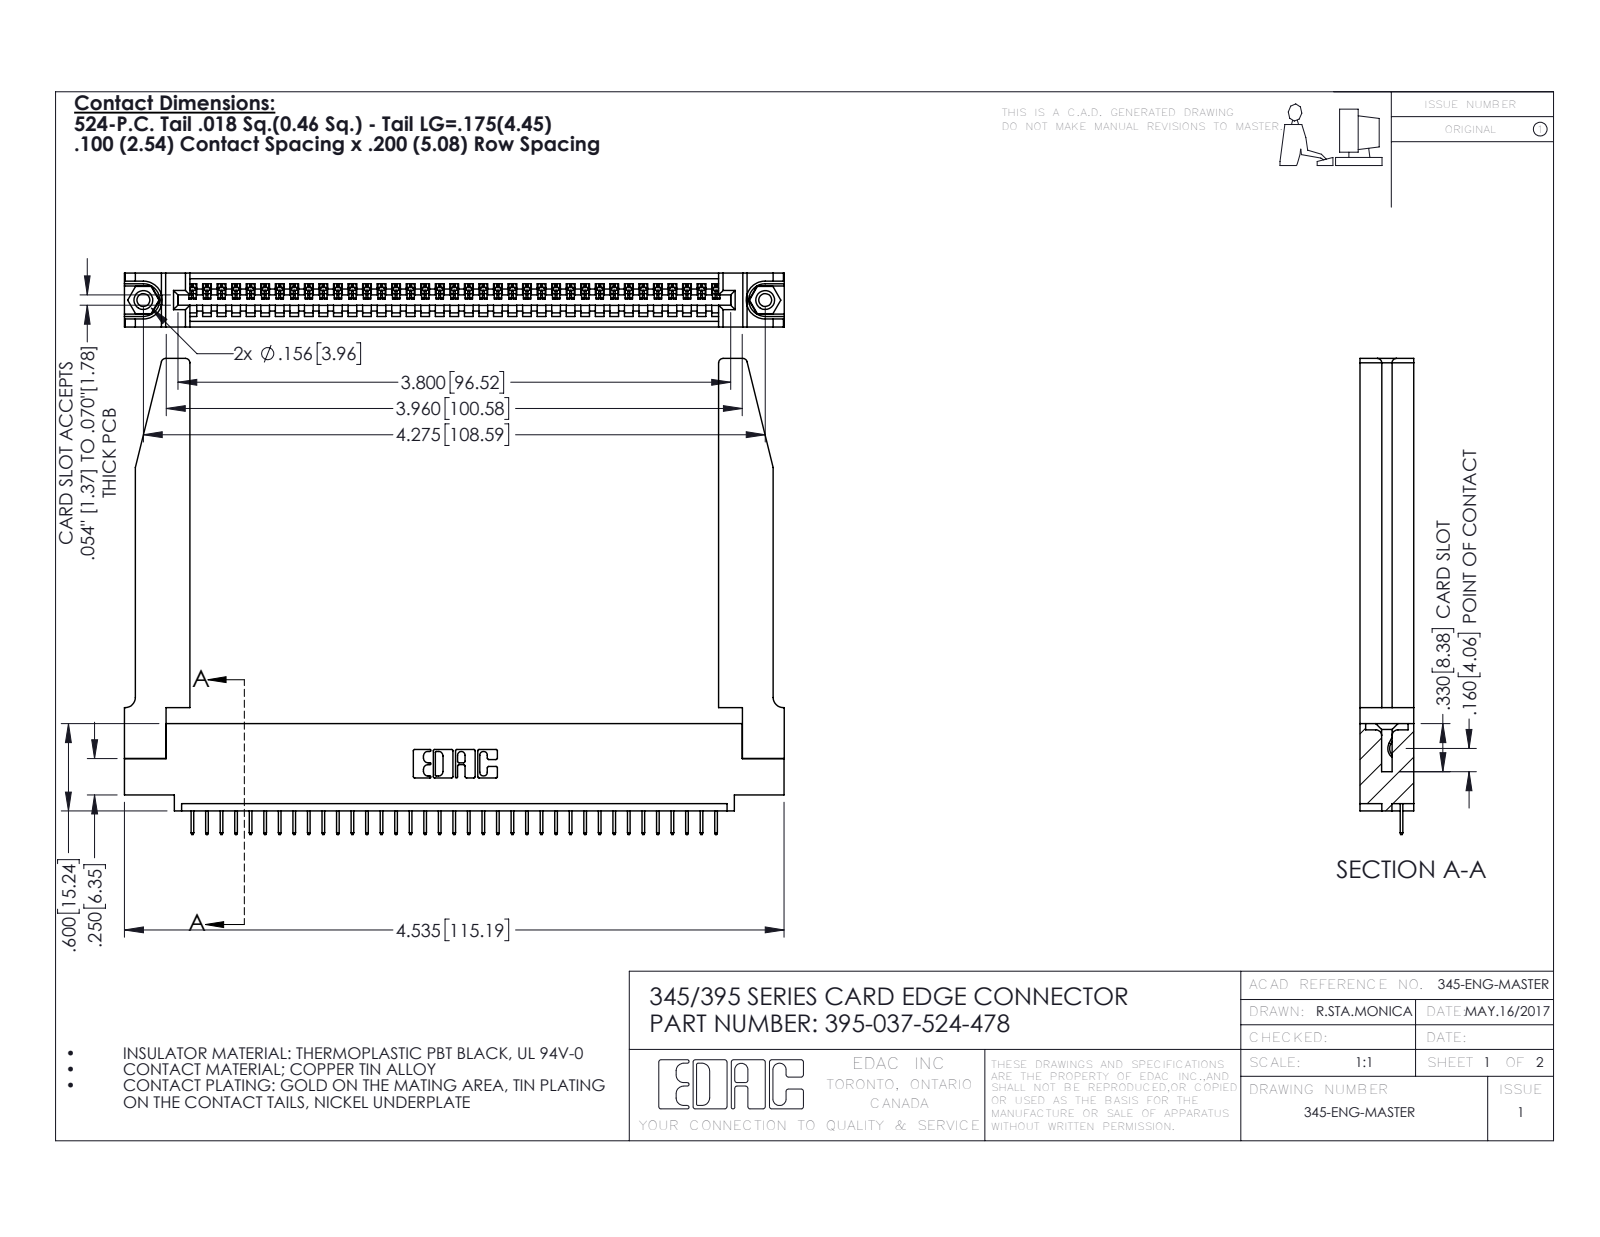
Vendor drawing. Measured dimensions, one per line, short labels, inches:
name: 345-220-078_345-220-078; 395-037-524-478; 345 Part_0.110 Offset - 0.156 Dia-TH; 345-292-001_345-293-124 (+1 more)
written by: SolidWorks 2016 (CONFIG_CONTROL_DESIGN)
unit: in
bodies: 42 solids, 2658 faces (1928 planar, 678 cylindrical, 52 other)
size: 4.536 × 3.272 × 0.37
volume: 1.126 in³; area: 31.91 in²
holes: 2× ⌀0.089, 2× ⌀0.125, 2× ⌀0.156, 1× ⌀0.064
bosses: 2× ⌀0.155
rounds: 74× R0.006, 22× R0.01, 8× R0.03, 6× R0.007, 6× R0.031, 3× R0.026, 2× R0.031, 2× R0.04
face distances: 0.37, 0.072, 0.298, 0.098, 0.272, 0.025, 0.2, 0.225, 0.15, 0.148
hole spacings: 0.27, 4.039, 4.275
